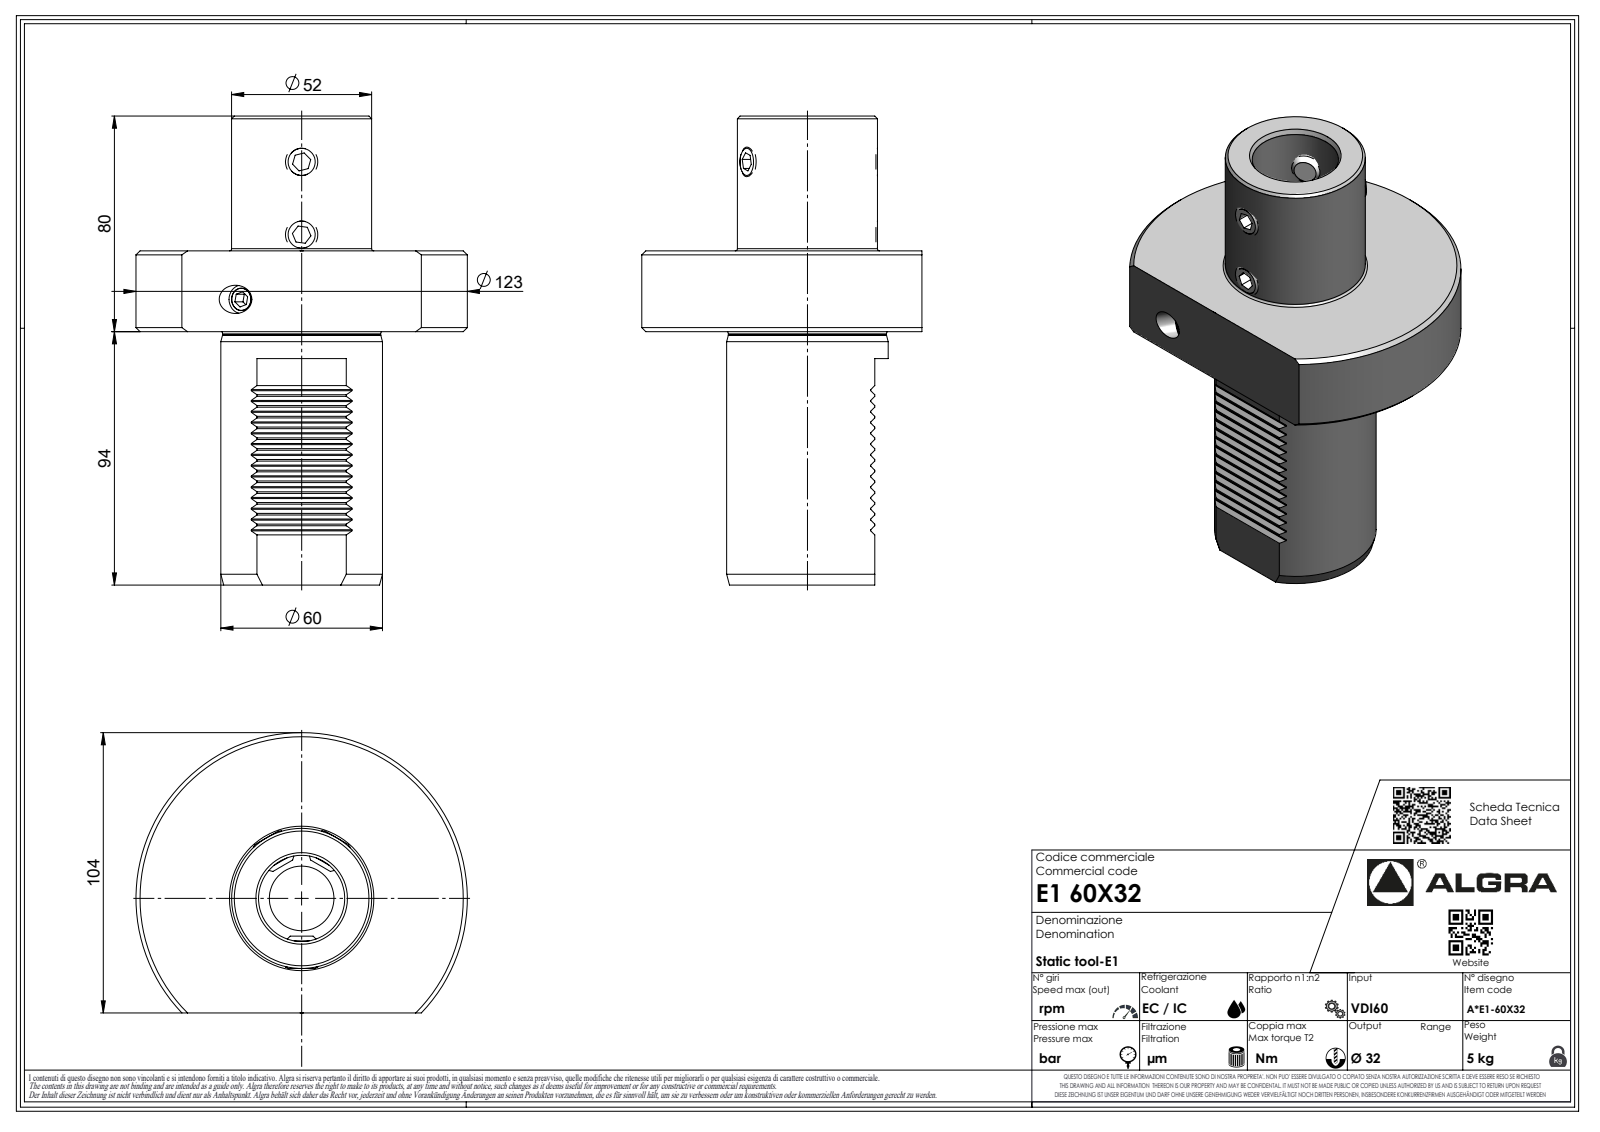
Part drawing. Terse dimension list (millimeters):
name: E160X32
written by: SolidWorks 2023 (AUTOMOTIVE_DESIGN)
unit: mm
bodies: 1 solid, 287 faces (189 planar, 45 cylindrical, 53 other)
size: 174 × 123 × 104
volume: 630 439 mm³; area: 64 777 mm²
holes: 1× ⌀2.1, 1× ⌀32
bosses: 1× ⌀60, 1× ⌀58.7, 1× ⌀52, 1× ⌀6.37, 1× ⌀1.7
rounds: 14× R0.3, 7× R0.33, 7× R0.52, 7× R3.7, 1× R0.21, 1× R61.5
face distances: 30, 94, 124, 2.83, 14.14, 11.31, 17.5, 174, 80, 50
